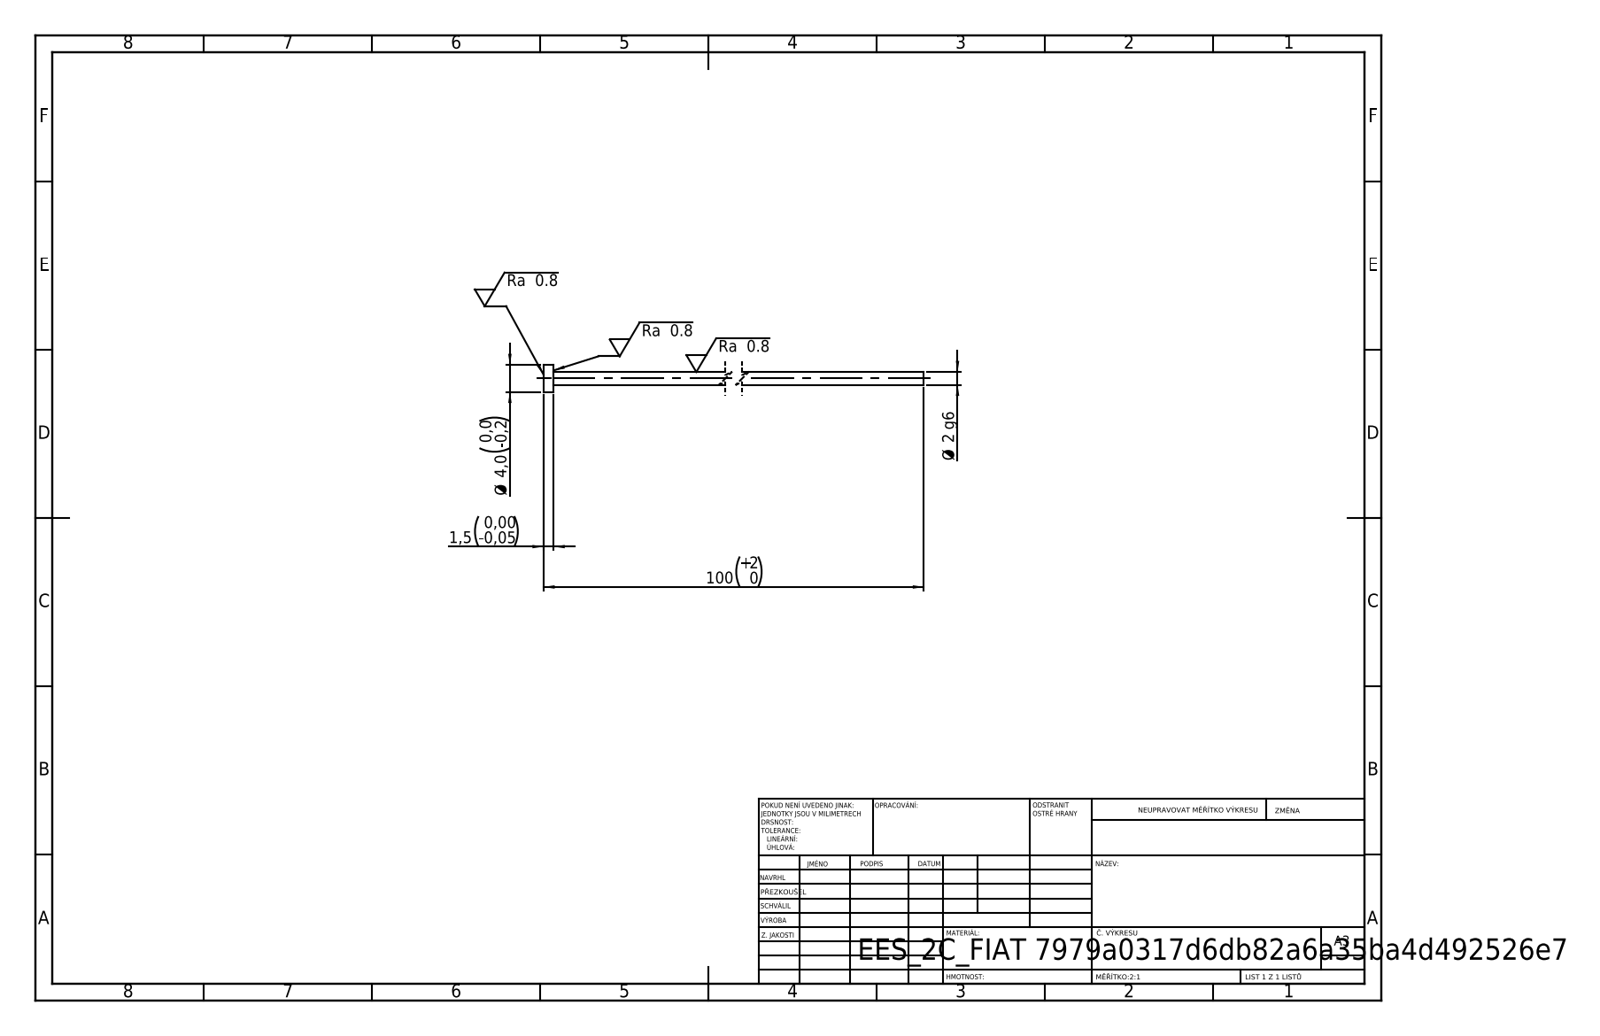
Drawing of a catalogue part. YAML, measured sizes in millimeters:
step_written_by: "SolidWorks 2019 (CONFIG_CONTROL_DESIGN)"
units: millimeters
bodies: {solids: 1, faces: 7, planar: 3, cylindrical: 4, other: 0}
overall_size: [100, 4, 4]
volume: 298
surface_area: 632
round_bosses_or_shafts:
  - {diameter: 4, count: 1}
  - {diameter: 1.9, count: 1}
face_to_face_distances: [1.5, 100, 98.5]
